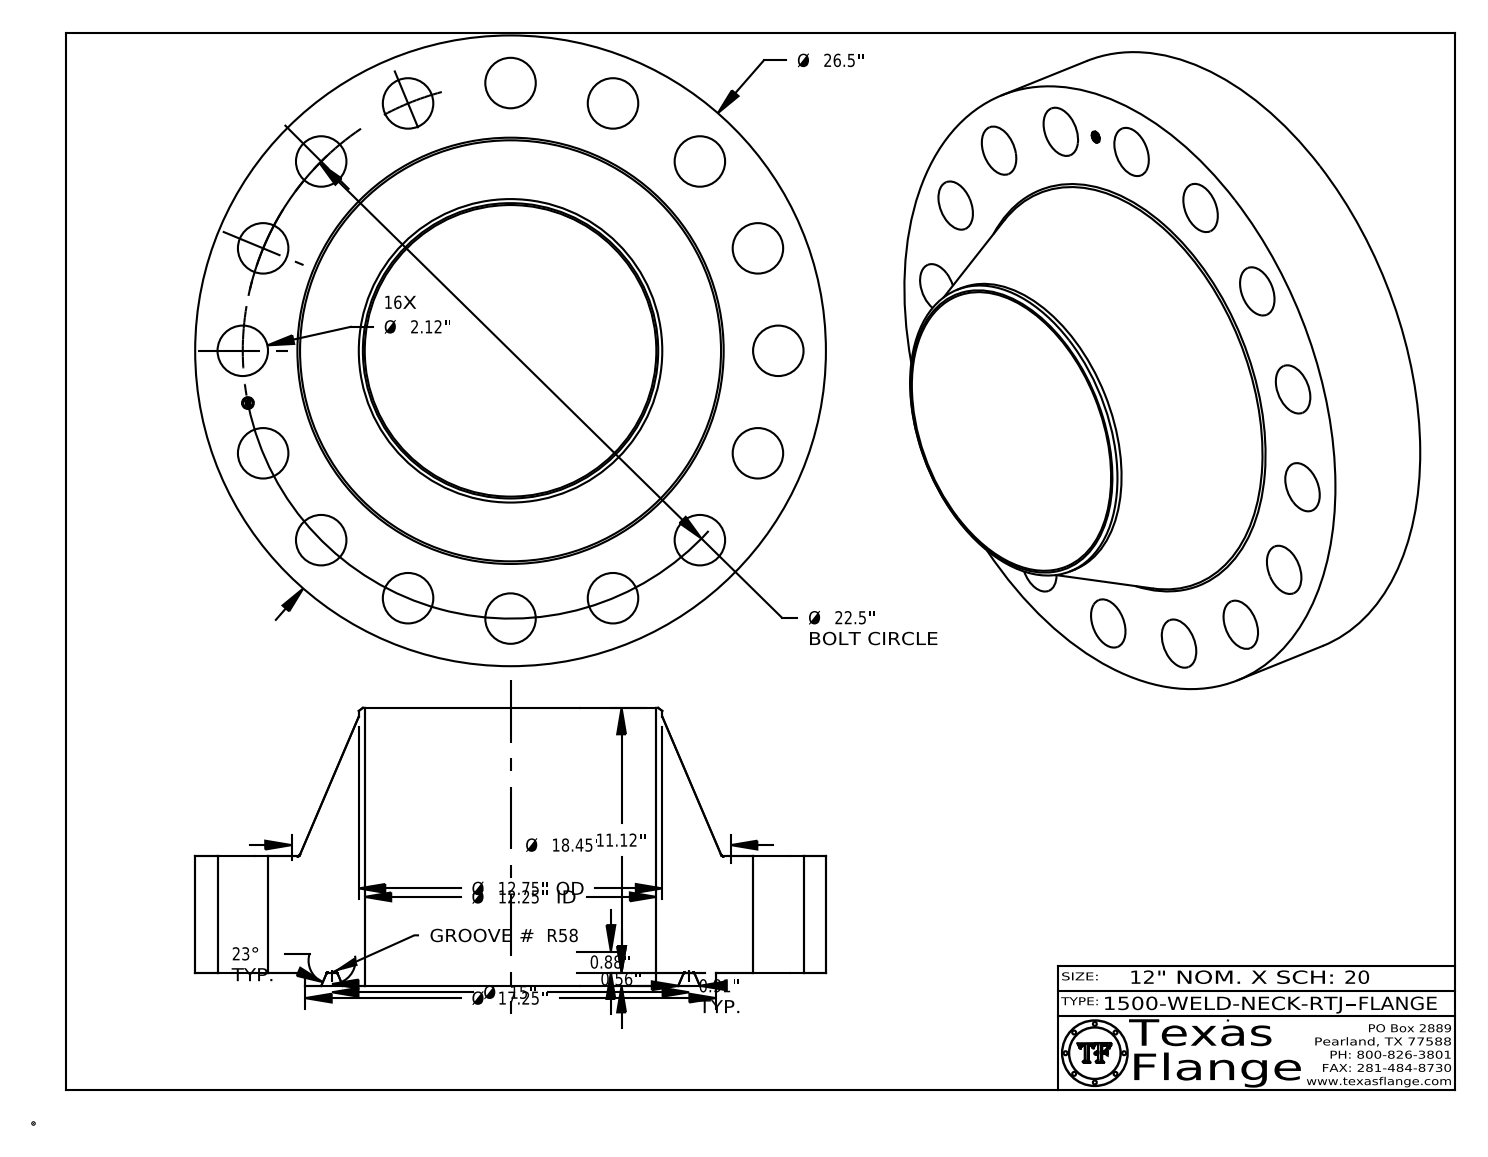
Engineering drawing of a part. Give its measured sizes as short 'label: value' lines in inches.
name: 1500-WELD-NECK-RTJ
written by: CATIA V5 STEP AP214 (AUTOMOTIVE_DESIGN)
unit: in
bodies: 1 solid, 445 faces (371 planar, 60 cylindrical, 14 other)
size: 26.5 × 26.5 × 11.683
volume: 2 282 in³; area: 2 391 in²
holes: 16× ⌀2.12, 1× ⌀0.495, 1× ⌀12.25
bosses: 8× ⌀0.03, 1× ⌀26.5, 1× ⌀17.25, 1× ⌀12.75, 1× ⌀0.39
face distances: 4.88, 0.563, 5.443, 11.683, 11.12, 6.24, 5.428, 4.865, 0.015, 6.255
hole spacings: 12.5, 20.787, 22.068, 11.25, 8.611, 15.91, 4.389, 4.39
